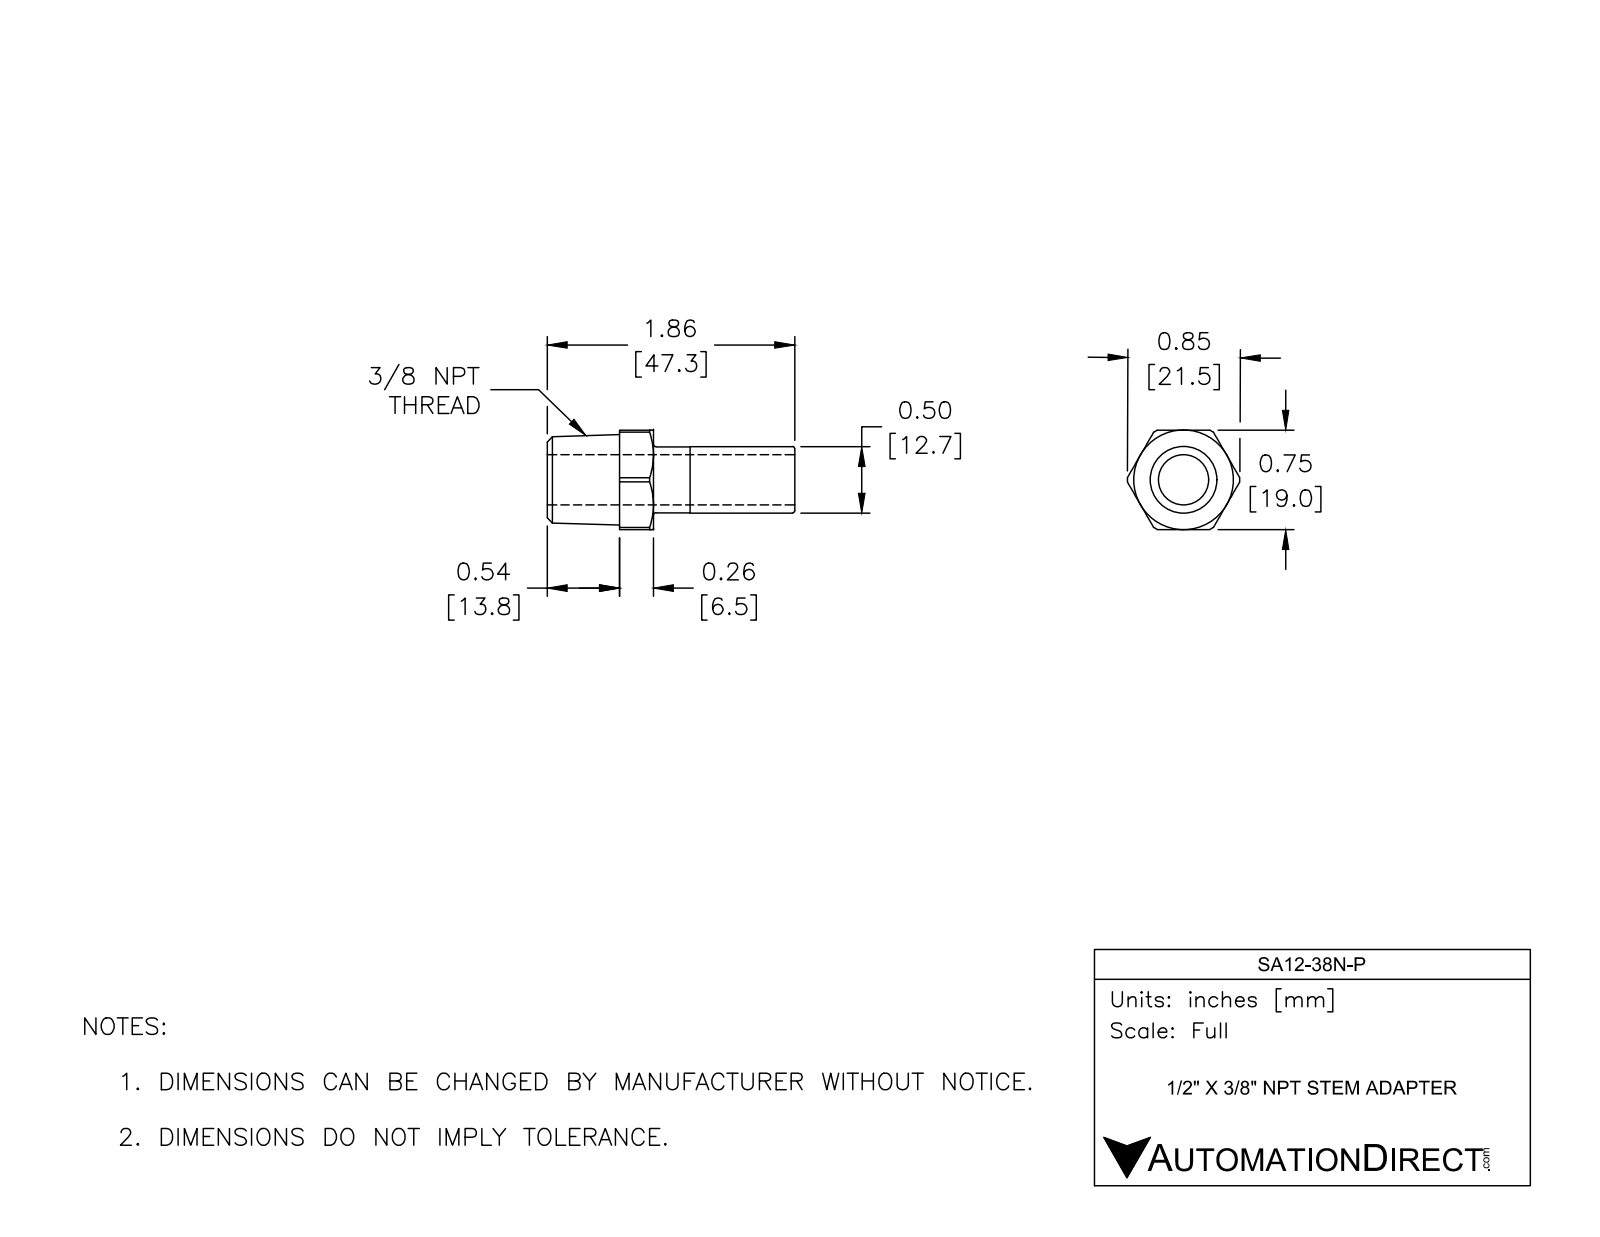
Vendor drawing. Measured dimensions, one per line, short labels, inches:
name: SA12-38N-P
written by: SolidWorks 2017 (AUTOMOTIVE_DESIGN)
unit: in
bodies: 1 solid, 39 faces (11 planar, 13 cylindrical, 15 other)
size: 1.862 × 0.846 × 0.748
volume: 0.309 in³; area: 6.289 in²
holes: 1× ⌀0.378
bosses: 1× ⌀0.5, 1× ⌀0.496
rounds: 1× R0.423
face distances: 0.748, 0.799, 0.543, 0.256, 1.862, 1.319, 1.063, 1.075, 0.531, 0.276
